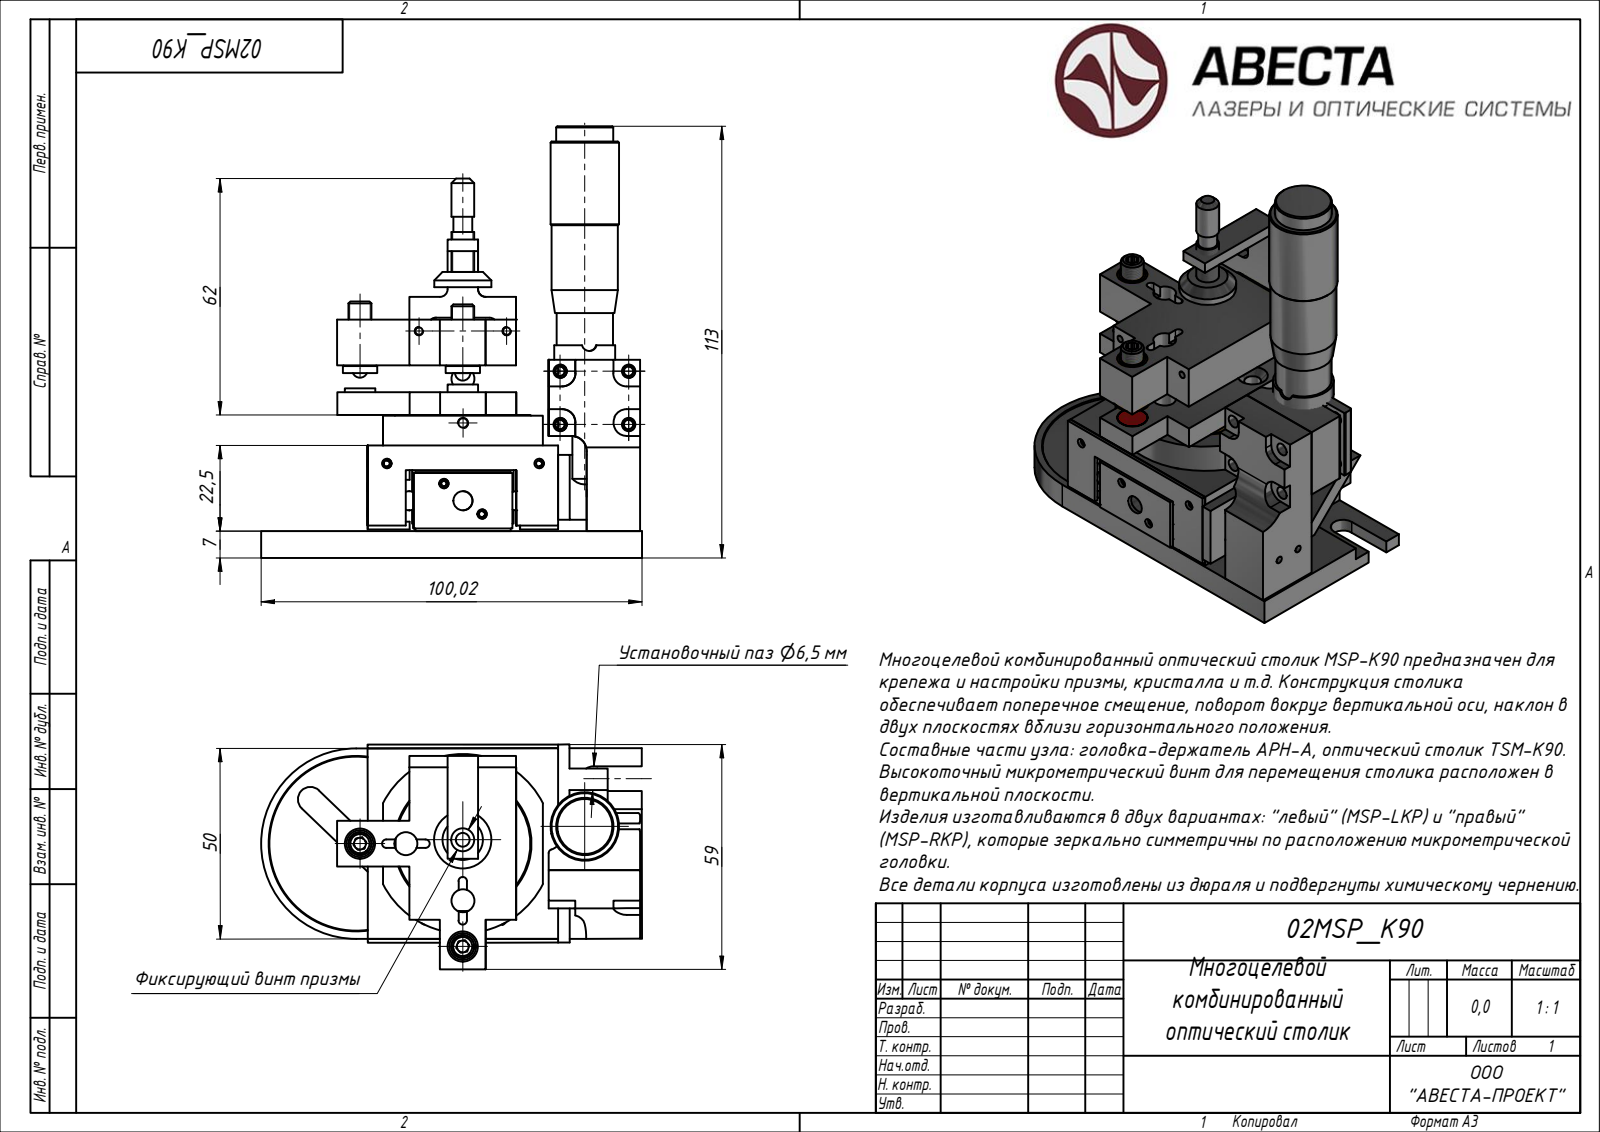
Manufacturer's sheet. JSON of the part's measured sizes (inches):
{"part_name": "Block 03; Block 01", "step_written_by": "ST-DEVELOPER v15 (AUTOMOTIVE_DESIGN)", "units": "inches", "bodies": {"solids": 23, "faces": 1265, "planar": 0, "cylindrical": 0, "other": 1265}, "overall_size": [4.459, 3.938, 2.497], "volume_in3": 0.048, "surface_area_in2": 103.3}
